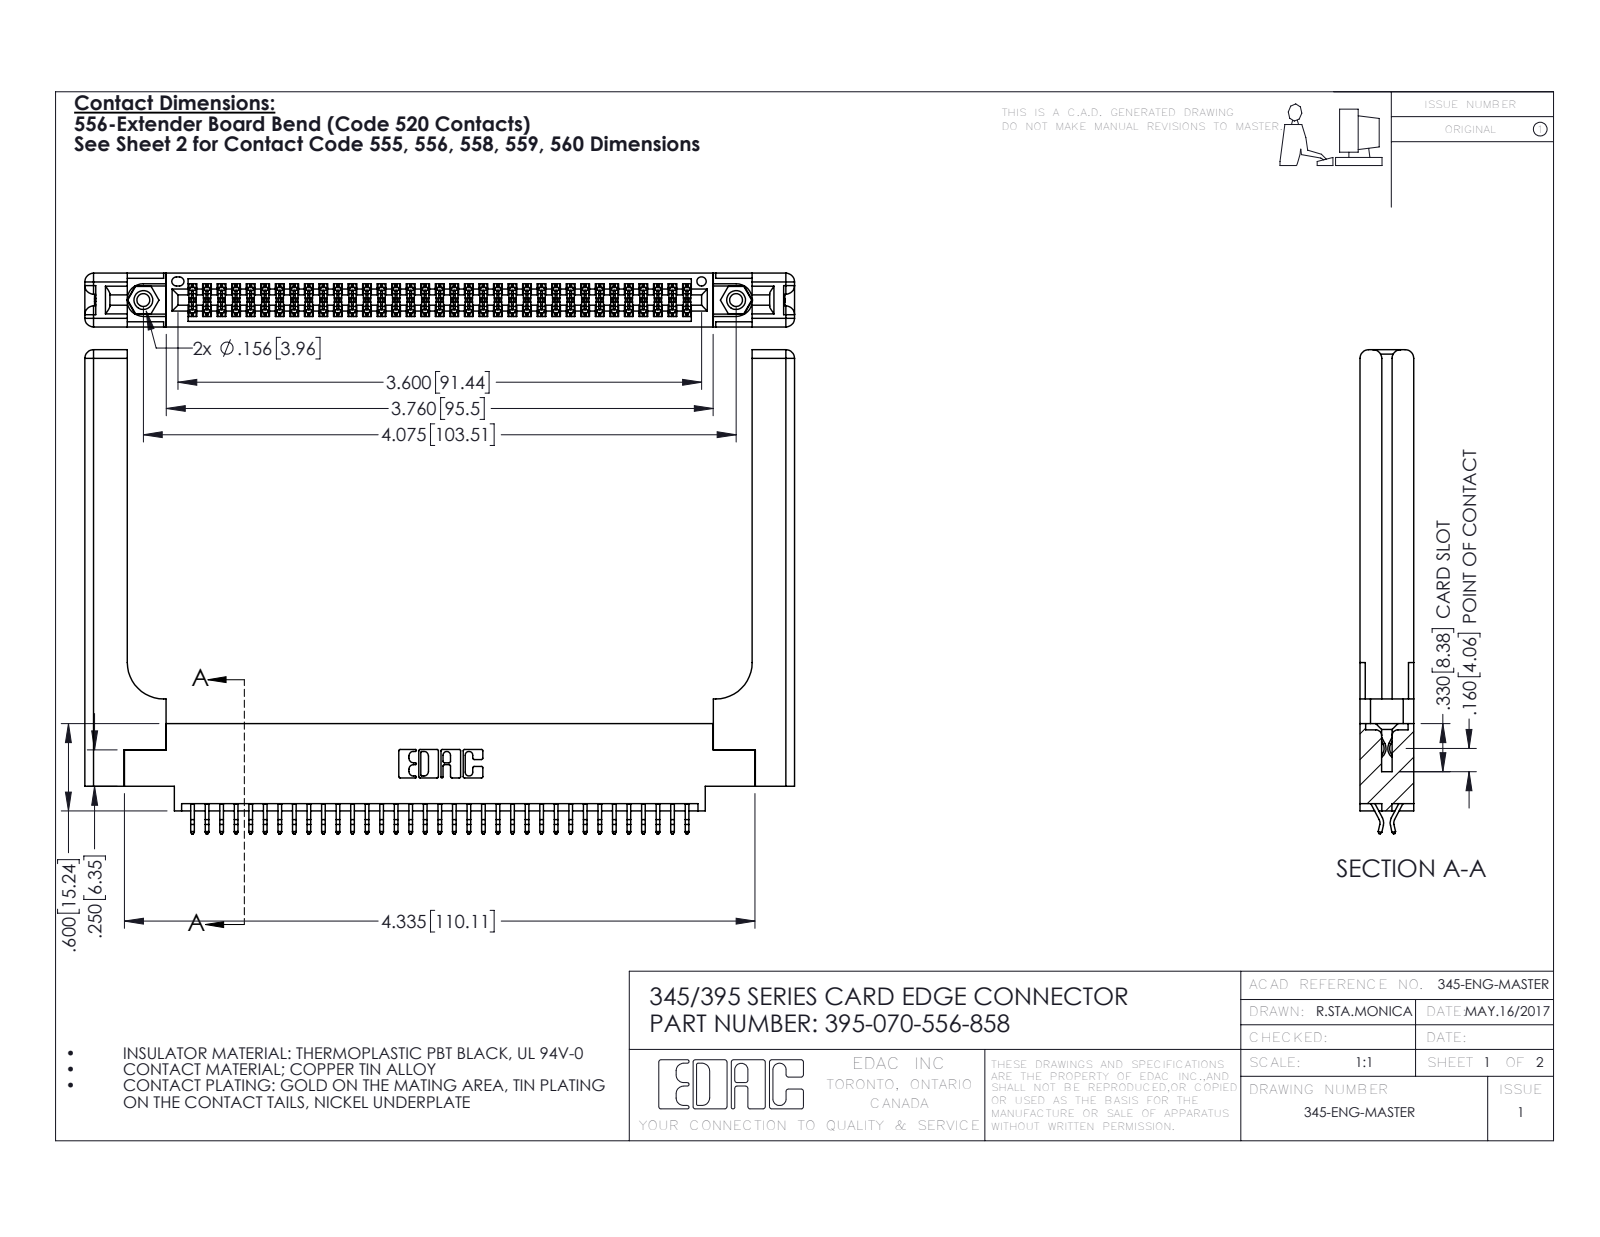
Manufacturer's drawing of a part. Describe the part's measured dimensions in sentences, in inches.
The part is named "395-070-556-858; 345-220-058_345-220-058; 345-250-001_345-250-001-102; 345-292-001_556 Tail (+1 more)". Its 3-D file was written by "SolidWorks 2016 (CONFIG_CONTROL_DESIGN)". It is 75 solids with 4306 faces: 2822 planar, 1424 cylindrical and 60 other. Overall it measures 4.879 by 3.327 by 0.37 inches. Its volume is 1.241 cubic inches and its surface area 34.93 square inches. Round holes: 2 of diameter 0.089, 2 of diameter 0.125, 2 of diameter 0.156, 1 of diameter 0.064. Round bosses or shafts: 2 of diameter 0.155. Partial cylindrical surfaces (rounded edges, fillets, slot ends): 105 of radius 0.006, 22 of radius 0.01, 16 of radius 0.06, 6 of radius 0.007, 6 of radius 0.031, 3 of radius 0.026, 2 of radius 0.01, 2 of radius 0.014. The main face-to-face distances are 0.37, 0.072, 0.298, 0.025, 0.098, 0.272, 0.2, 0.225, 0.148, 0.15. The hole center spacings are 0.27, 3.839, 4.075.
